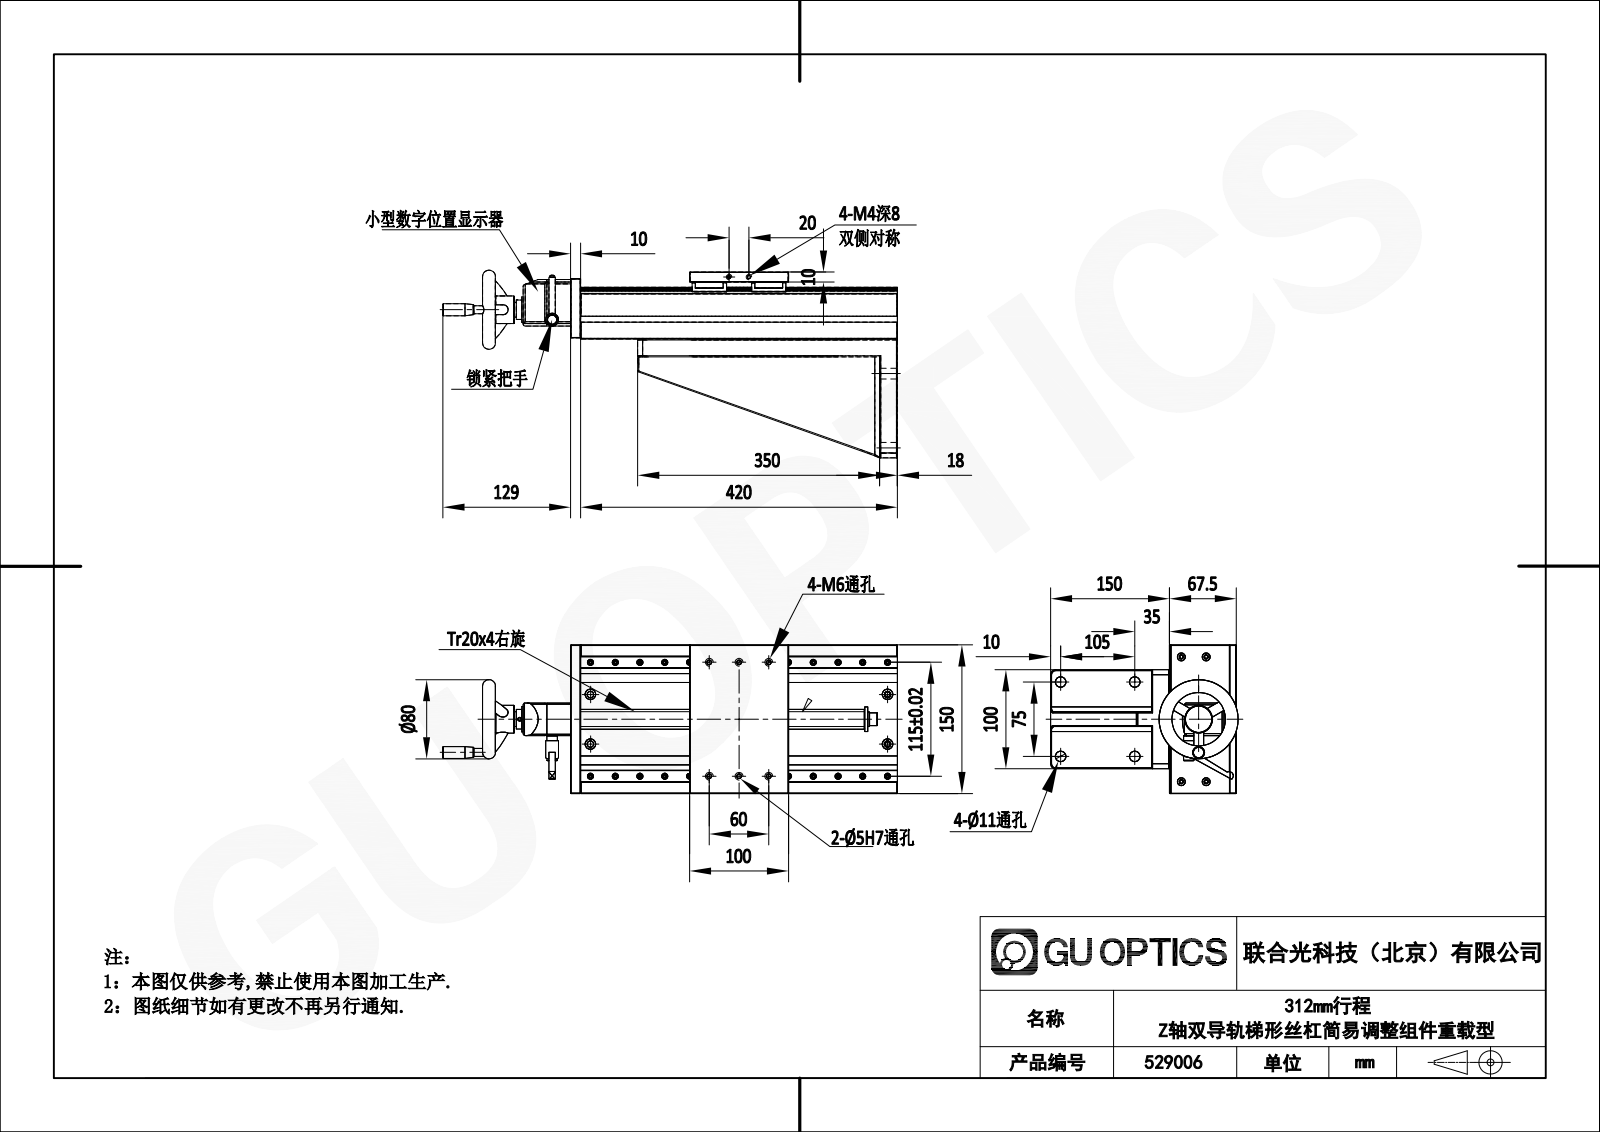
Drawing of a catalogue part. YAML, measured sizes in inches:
part_name: "DHQ46-420-C"
step_written_by: "SolidWorks 2023 (CONFIG_CONTROL_DESIGN)"
units: inches
bodies: {solids: 0, faces: 1004, planar: 258, cylindrical: 681, other: 65}
overall_size: [22.5, 8.76, 5.906]
round_holes:
  - {diameter: 0.236, count: 33}
  - {diameter: 0.256, count: 16}
  - {diameter: 0.197, count: 15}
  - {diameter: 0.433, count: 12}
  - {diameter: 0.194, count: 6}
  - {diameter: 0.394, count: 5}
  - {diameter: 0.315, count: 4}
  - {diameter: 0.098, count: 2}
  - {diameter: 0.13, count: 2}
  - {diameter: 0.157, count: 2}
  - {diameter: 0.26, count: 2}
round_bosses_or_shafts:
  - {diameter: 1.063, count: 1}
  - {diameter: 0.945, count: 1}
  - {diameter: 0.787, count: 1}
  - {diameter: 0.78, count: 1}
  - {diameter: 0.61, count: 1}
  - {diameter: 0.551, count: 1}
  - {diameter: 0.512, count: 1}
  - {diameter: 0.413, count: 1}
partial_cylinders:
  - {radius: 0.184, count: 15}
  - {radius: 0.276, count: 11}
  - {radius: 0.039, count: 10}
  - {radius: 0.079, count: 9}
  - {radius: 0.052, count: 4}
  - {radius: 0.197, count: 4}
  - {radius: 0.118, count: 2}
  - {radius: 0.02, count: 1}
face_to_face_distances: [0.394, 2.657, 2.264, 1.102, 0.709, 0.591, 0.453, 1.673, 3.248, 0.472]
hole_center_spacings: [1.969, 0.984, 3.937, 2.953, 5.906, 4.633, 7.874, 2.348]
